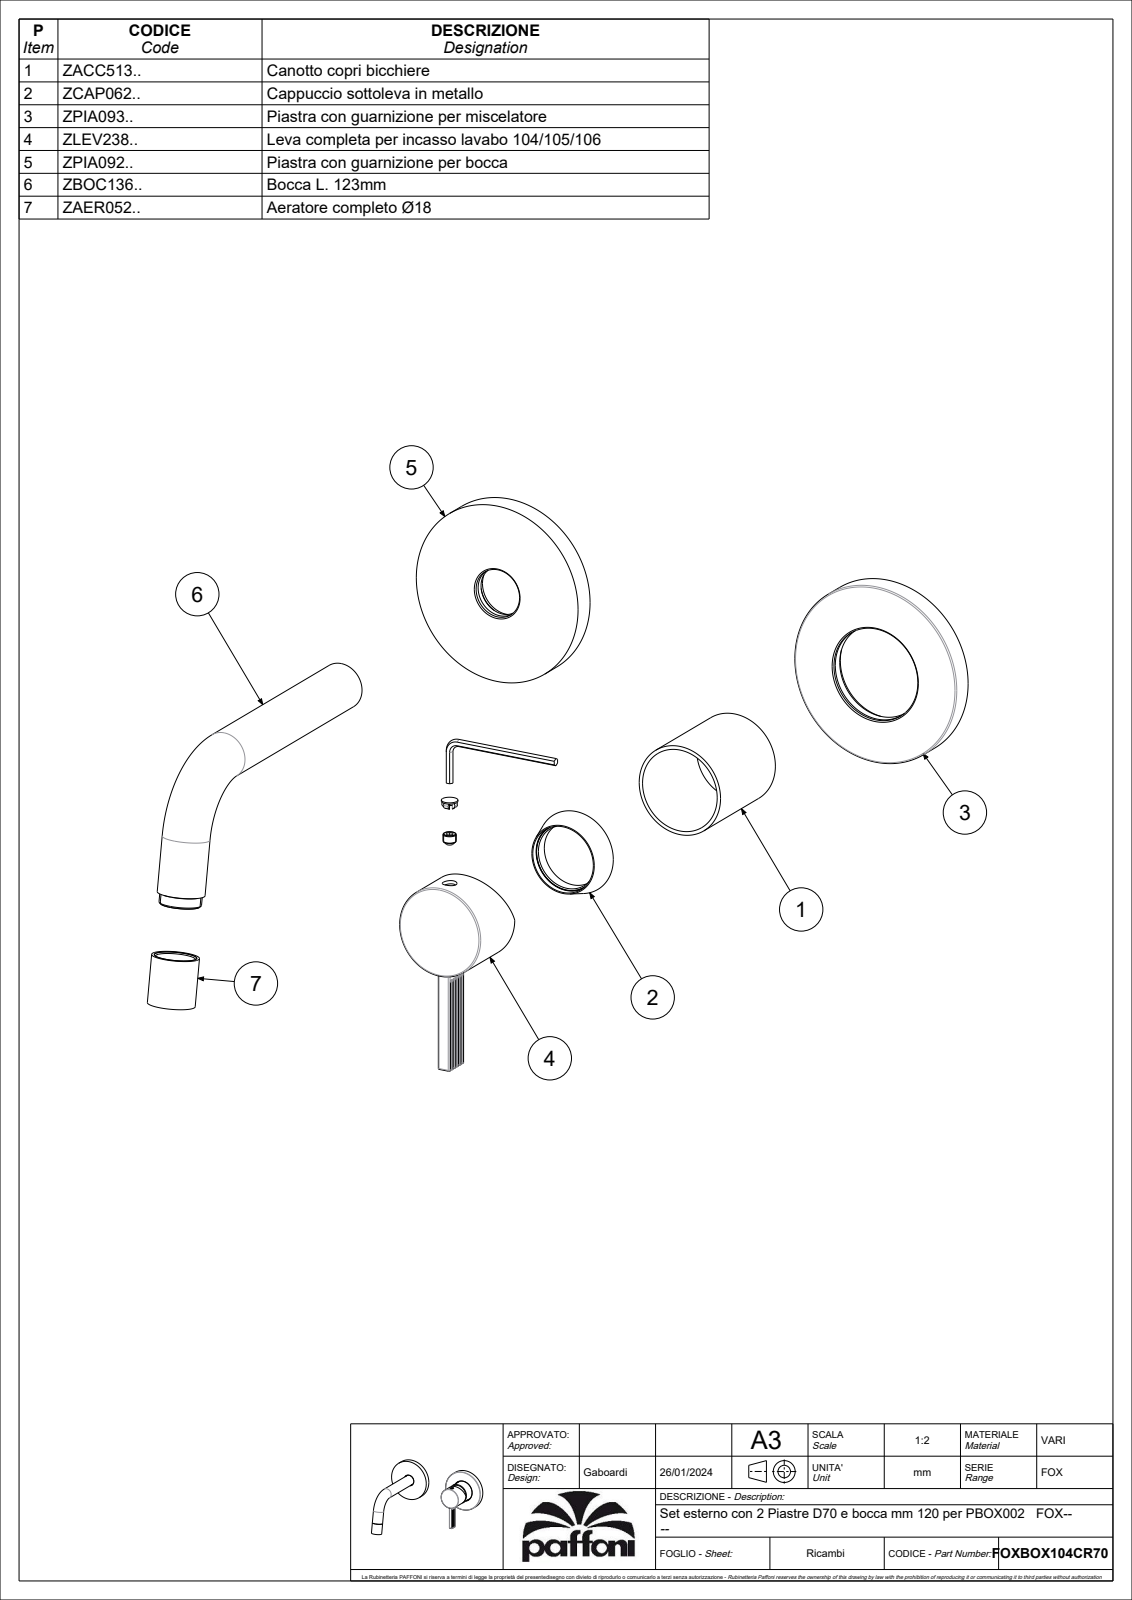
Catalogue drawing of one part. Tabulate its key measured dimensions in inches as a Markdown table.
| quantity | value |
| --- | --- |
| part name | FOX104CR70 |
| STEP written by | CREO PARAMETRIC BY PTC INC, 2022124 (CONFIG_CONTROL_DESIGN) |
| units | inches |
| bodies | 4 solids, 1112 faces (261 planar, 570 cylindrical, 281 other) |
| overall size | 7.047 × 5.023 × 3.928 |
| volume | 5.278 in³ |
| surface area | 103.1 in² |
| round holes (diameter × count) | 0.02 × 51, 0.165 × 2, 0.394 × 2, 0.433 × 2, 0.472 × 2, 2.559 × 2, 0.118 × 1, 0.119 × 1, 0.126 × 1, 0.217 × 1, 0.236 × 1, 0.492 × 1 |
| round bosses / shafts (diameter × count) | 2.756 × 2, 0.709 × 2, 1.783 × 1, 1.386 × 1, 1.378 × 1, 1.181 × 1, 1.094 × 1, 1.091 × 1 |
| partial cylindrical surfaces (radius × count) | 0.012 × 50, 0.02 × 47, 0.039 × 14, 0.016 × 13, 0.004 × 8, 0.118 × 6, 0.059 × 2, 0.079 × 1 |
| main face-to-face distances | 0.079, 0.354, 0.276, 0.059, 0.295, 0.02, 0.217, 0.039, 0.236, 0.425 |
| hole center spacings | 0.059, 0.132, 0.132, 0.213, 0.083, 0.187, 0.244, 0.177 |
